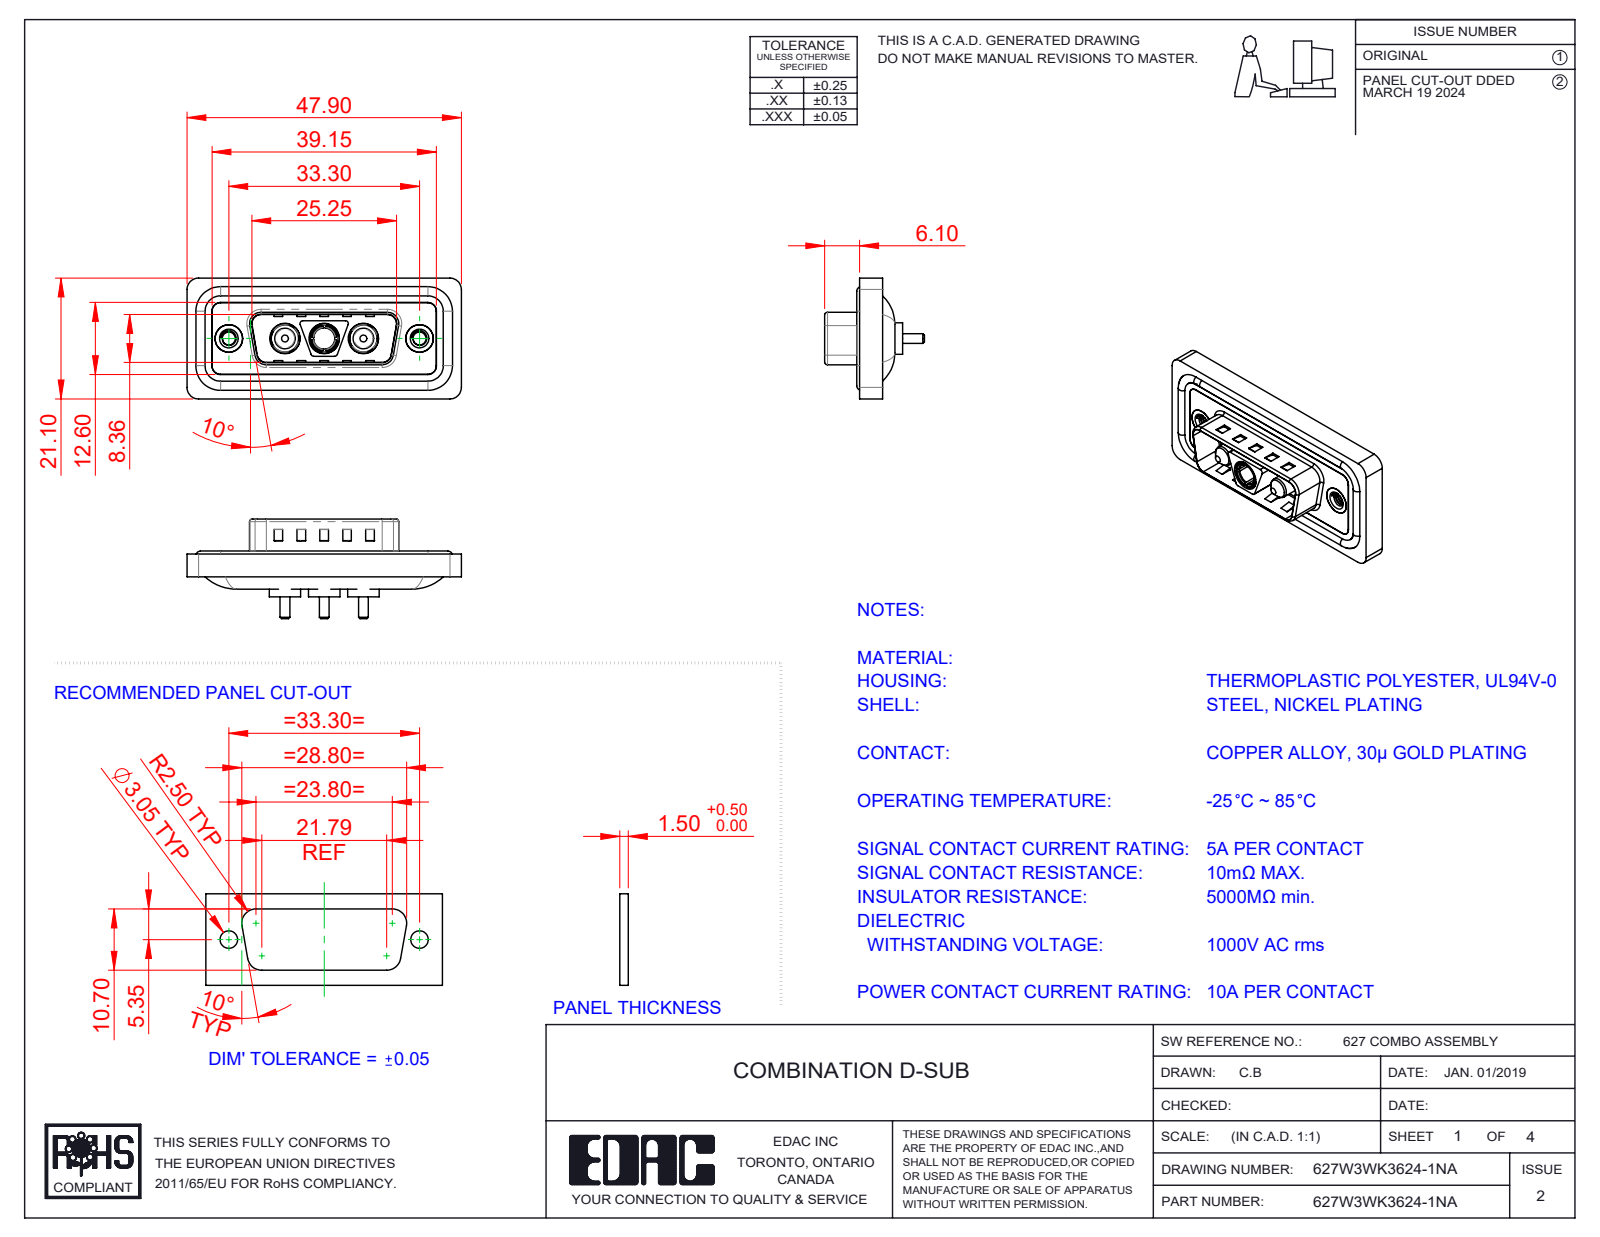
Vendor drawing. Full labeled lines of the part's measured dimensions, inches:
Part name (STEP PRODUCT): 627Combo Shell Rear_15 Contacts; Power Pin_10A S; 627Combo Waterproof Housing_15 Contacts; Power Socket_10A S (+4 more)
STEP written by: SolidWorks 2023 (CONFIG_CONTROL_DESIGN)
Units: inches
Bodies: 13 solids, 607 faces (231 planar, 252 cylindrical, 124 other)
Overall size (bounding box): 1.886 × 0.831 × 0.685
Volume: 0.345 in³ · Surface area: 14.08 in²
Round holes (diameter × count): ⌀0.191 ×3, ⌀0.209 ×3, ⌀0.089 ×2, ⌀0.157 ×2, ⌀0.189 ×2, ⌀0.197 ×2, ⌀0.146 ×1
Round bosses / shafts (diameter × count): ⌀0.063 ×4, ⌀0.217 ×3, ⌀0.205 ×3, ⌀0.187 ×3, ⌀0.148 ×3, ⌀0.067 ×3, ⌀0.193 ×2, ⌀0.142 ×2
Partial cylindrical surfaces — rounded edges, fillets, slot ends (radius × count): R0.059 ×26, R0.079 ×20, R0.02 ×12, R0.063 ×8, R0.01 ×4, R0.024 ×4, R0.026 ×4, R0.035 ×4
Main face-to-face distances: 0.016, 0.059, 0.043, 0.02, 0.063, 0.122, 0.114, 0.157, 0.032, 0.377
Hole centre spacings: 0.27, 0.386, 0.656, 0.925, 0.539, 1.311
